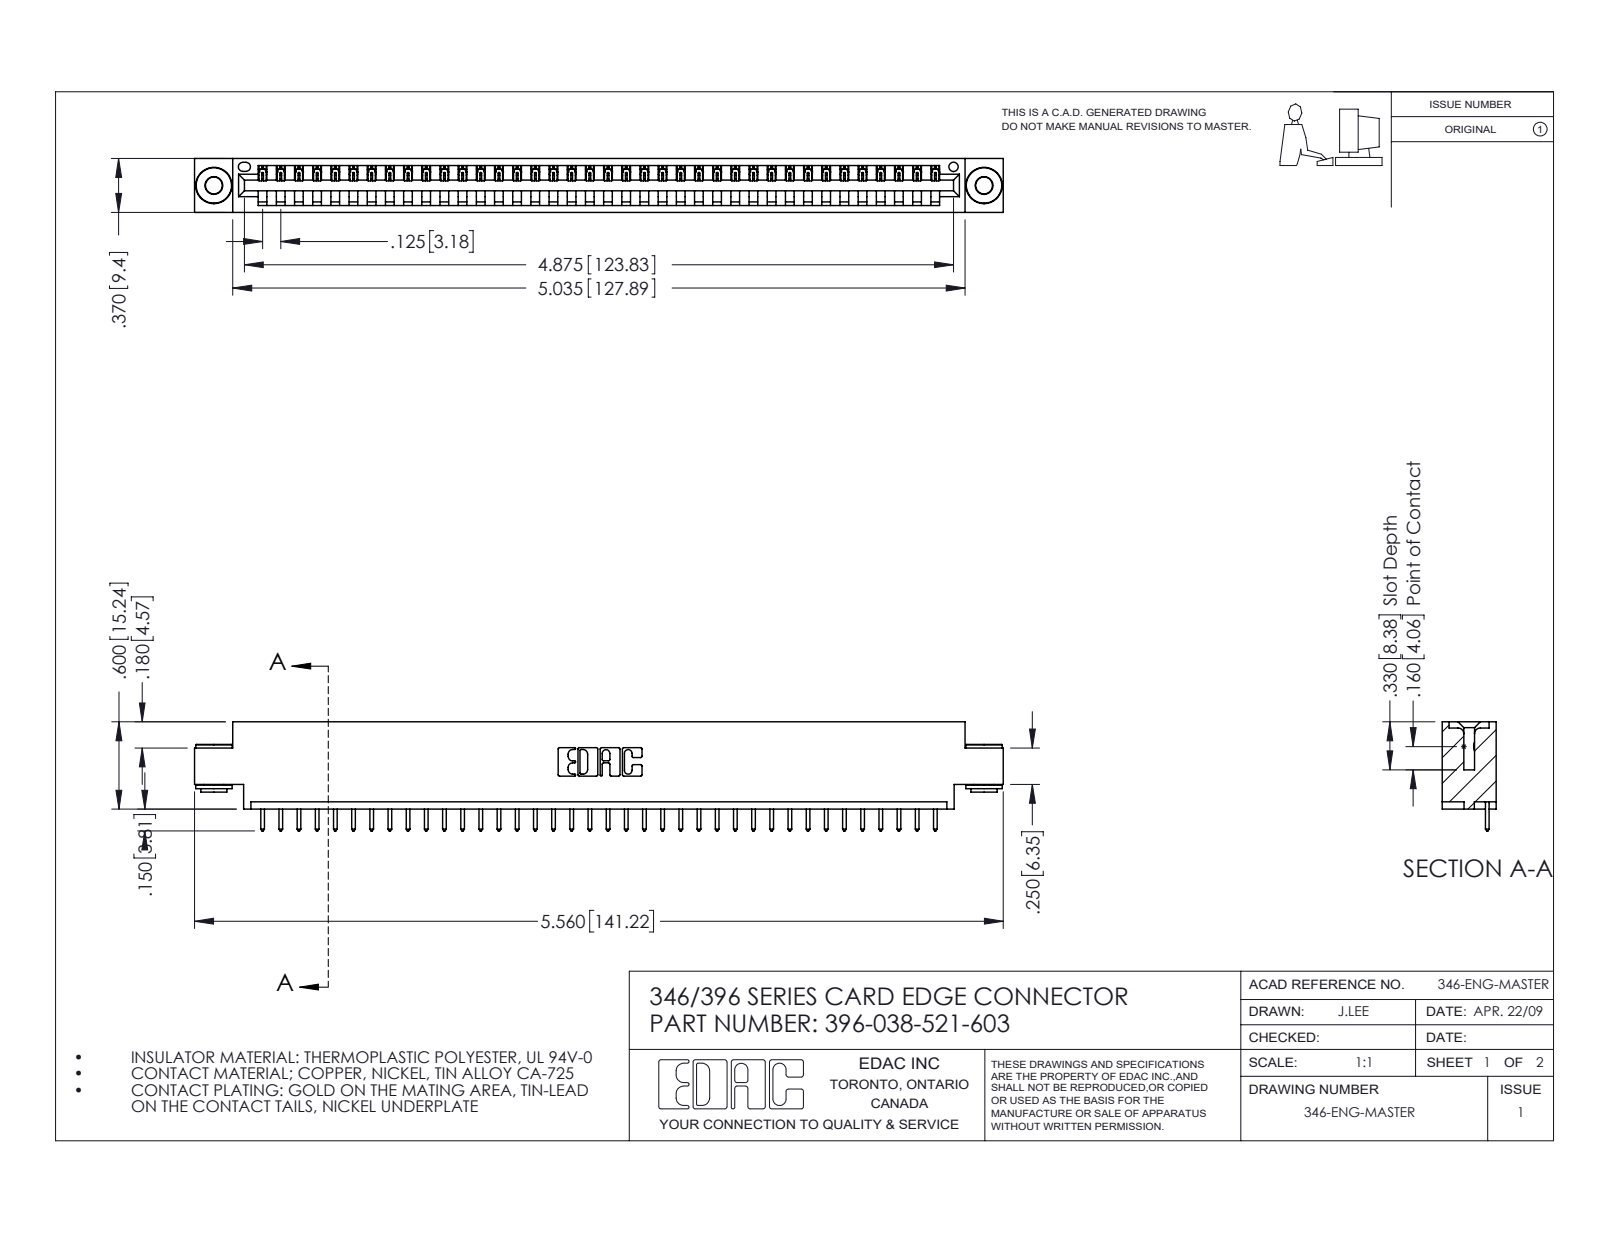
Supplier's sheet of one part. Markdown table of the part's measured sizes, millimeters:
| quantity | value |
| --- | --- |
| part name | 345-250-002_345-250-002-102; 345-292-001_345-293-121; 346 Part_0.170 Offset - 0.156 Dia-TH; 396-038-521-603 |
| STEP written by | SolidWorks 2016 (CONFIG_CONTROL_DESIGN) |
| units | millimeters |
| bodies | 41 solids, 2368 faces (1610 planar, 750 cylindrical, 8 other) |
| overall size | 141.2 × 19.1 × 9.4 |
| volume | 13 200 mm³ |
| surface area | 16 460 mm² |
| round holes (diameter × count) | 2.9 × 2, 4 × 2, 1.6 × 1 |
| round bosses / shafts (diameter × count) | 6.4 × 2, 4.6 × 2, 3.5 × 2 |
| partial cylindrical surfaces (radius × count) | 0.2 × 76, 0.3 × 76, 0.3 × 22, 0.2 × 6, 0.8 × 6, 0.7 × 3, 0.8 × 2, 1 × 2 |
| main face-to-face distances | 1.2, 8.2, 9.4, 6.4, 0.6, 1.8, 7.6, 3.8, 5.6, 2.5 |
| hole center spacings | 6.2, 129.2, 134.5 |
